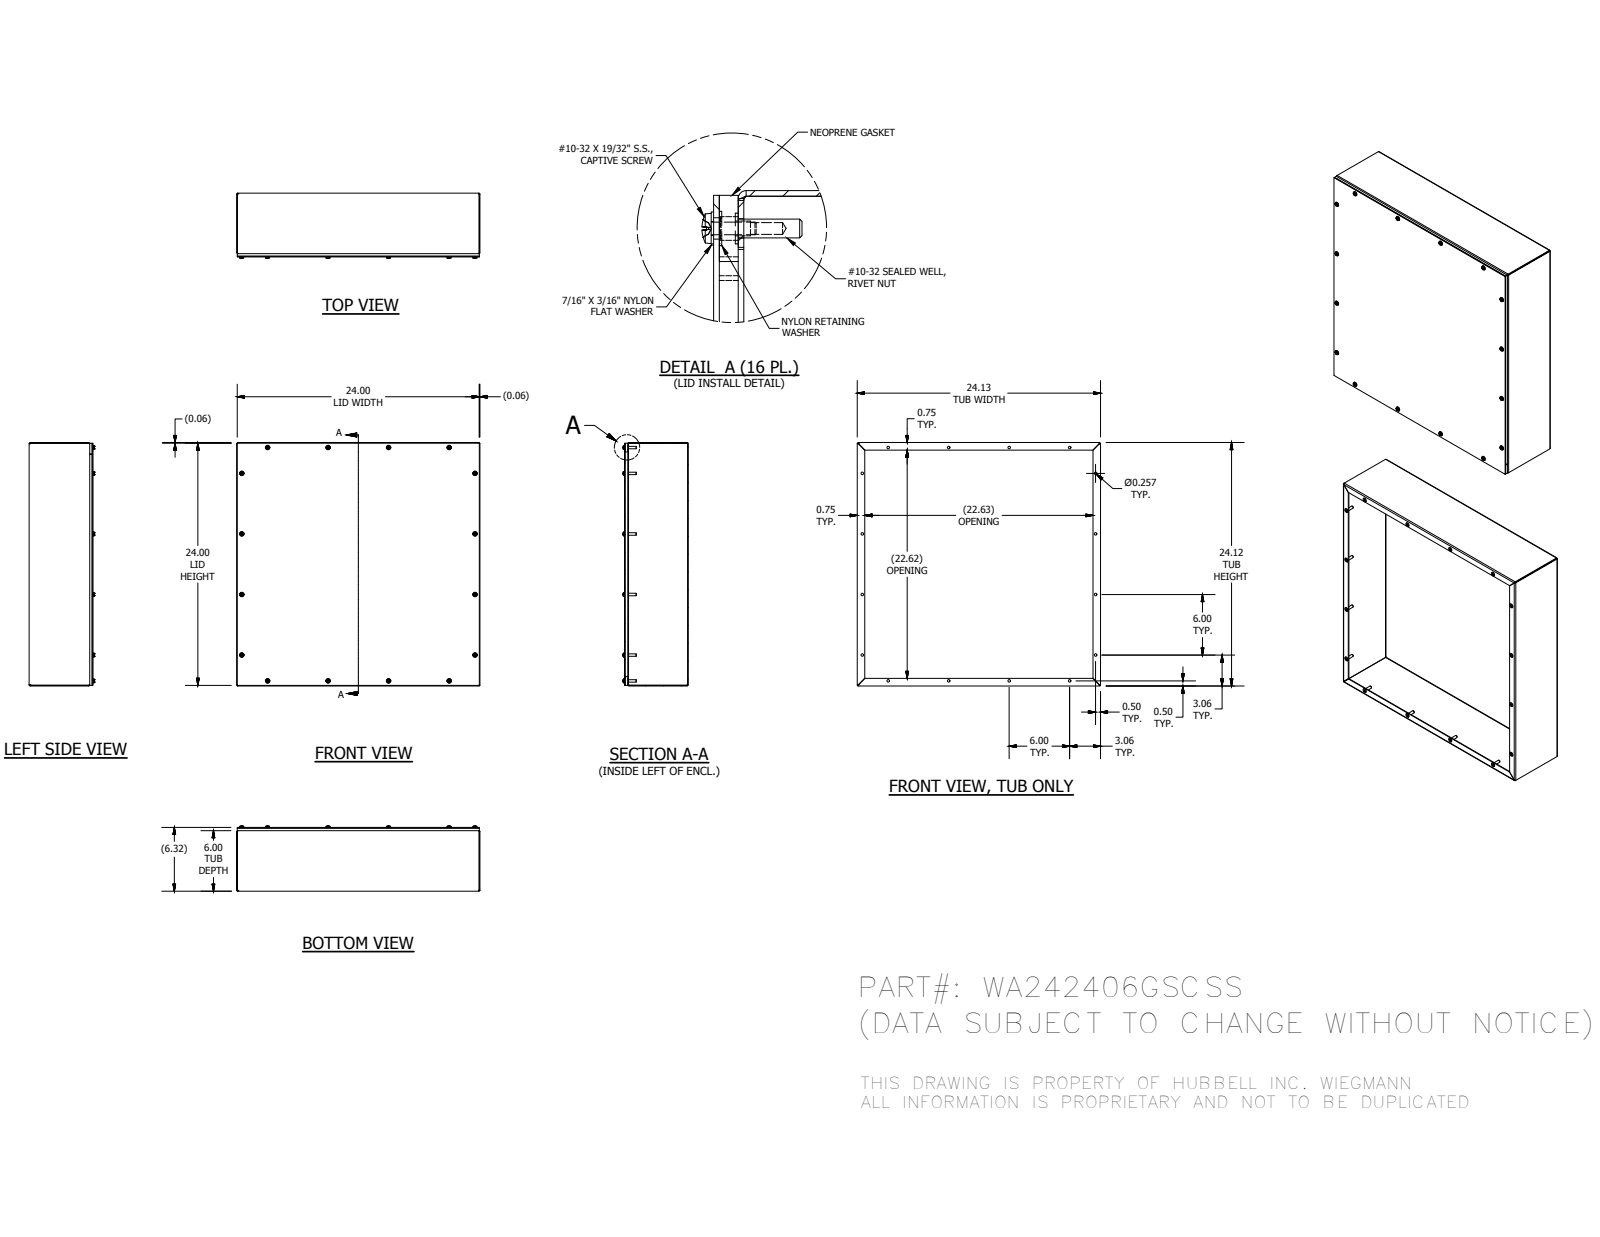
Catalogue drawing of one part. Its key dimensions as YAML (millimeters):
part_name: "WA242406GSCSSBKP; WA2424GSCSSLID; 37210; 39035 (+4 more)"
step_written_by: "Autodesk Inventor 2016 (AUTOMOTIVE_DESIGN)"
units: millimeters
bodies: {solids: 68, faces: 1412, planar: 772, cylindrical: 288, other: 352}
overall_size: [612.77, 612.77, 164.56]
volume: 2504000
surface_area: 2475000
round_holes:
  - {diameter: 3.96, count: 16}
  - {diameter: 4.78, count: 16}
  - {diameter: 4.98, count: 16}
  - {diameter: 6.53, count: 16}
  - {diameter: 7.06, count: 16}
  - {diameter: 7.14, count: 16}
  - {diameter: 7.95, count: 16}
round_bosses_or_shafts:
  - {diameter: 11.51, count: 16}
  - {diameter: 11.11, count: 16}
  - {diameter: 10.31, count: 16}
  - {diameter: 6.3, count: 16}
  - {diameter: 4.25, count: 16}
partial_cylinders:
  - {radius: 2.27, count: 16}
  - {radius: 0.79, count: 12}
  - {radius: 1.78, count: 8}
  - {radius: 2.67, count: 8}
face_to_face_distances: [1.88, 158.75, 160.63, 156.87, 610.9, 609.02, 612.78, 150.52, 8.23, 6.35]
hole_center_spacings: [152.4, 304.8, 606.81, 227.02, 375.57, 429.08, 526.33, 565.76]
